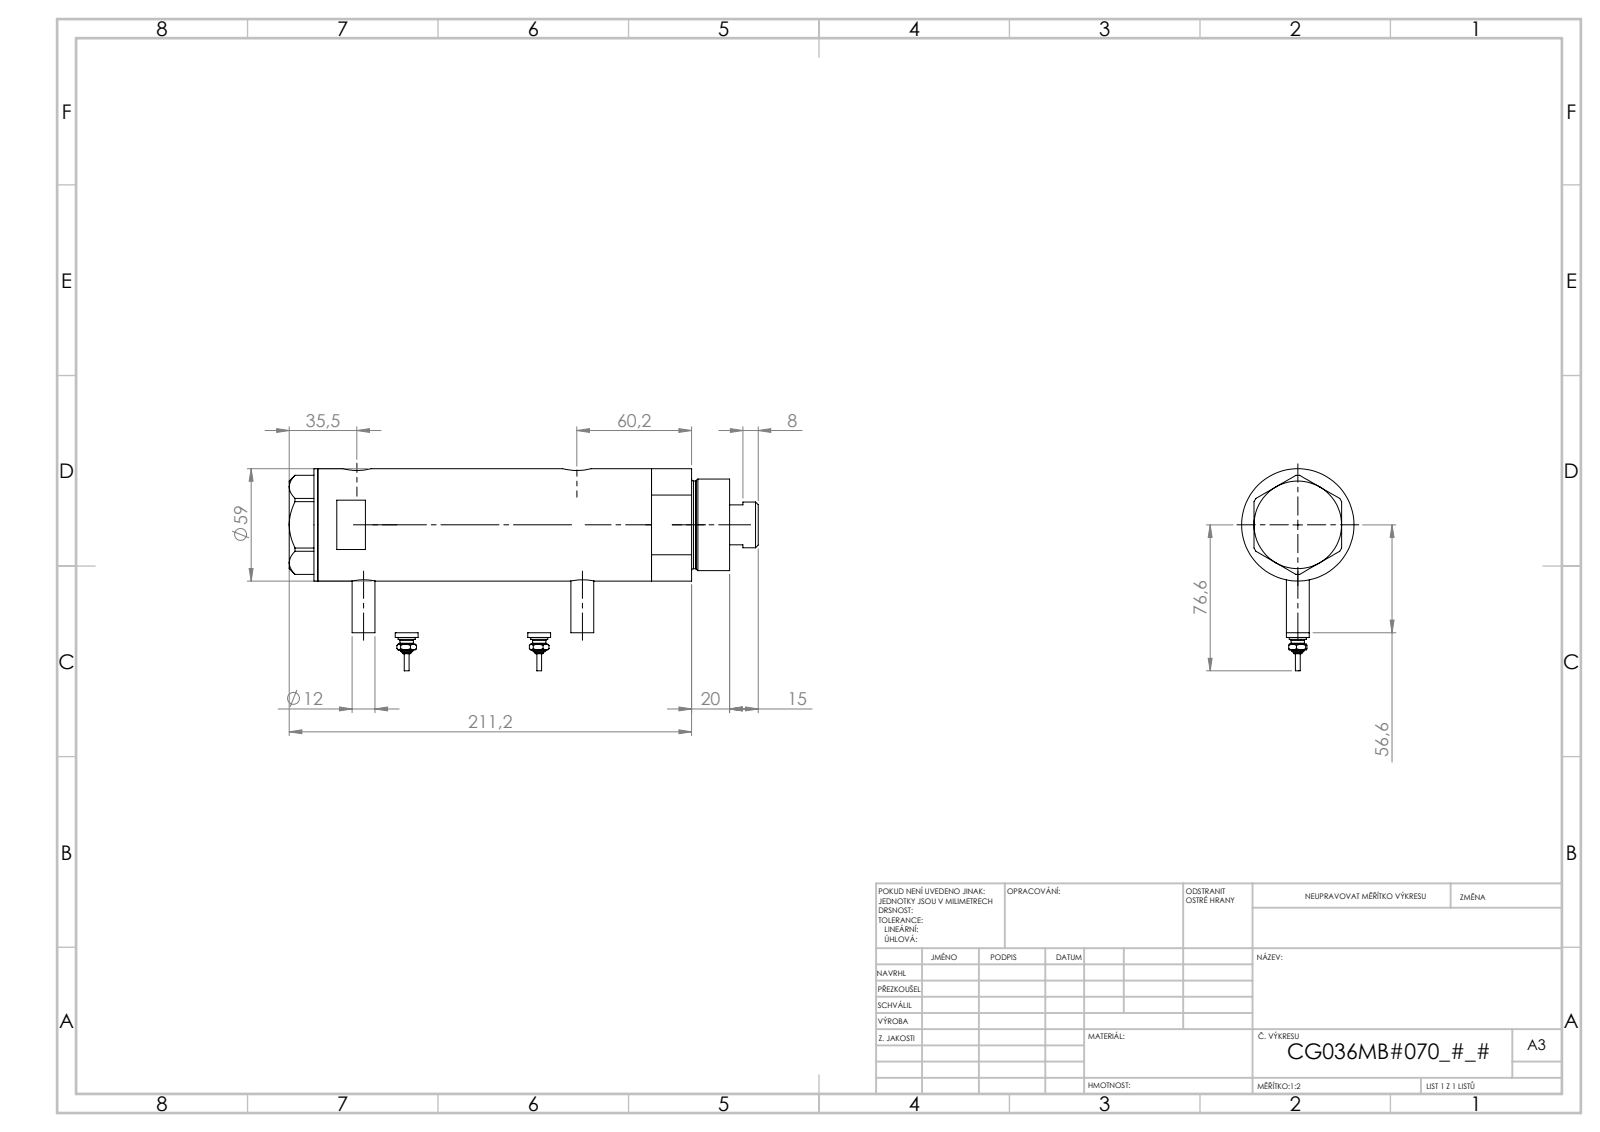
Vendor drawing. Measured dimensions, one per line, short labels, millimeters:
name: V270CG_SWITCH; V270CG_MIDDLE; V270CG_FRONT; V270CG_BACK (+1 more)
written by: SolidWorks 2019 (CONFIG_CONTROL_DESIGN)
unit: mm
bodies: 6 solids, 232 faces (81 planar, 77 cylindrical, 74 other)
size: 233.42 × 91.3 × 59
volume: 528 486 mm³; area: 110 229 mm²
holes: 2× ⌀5, 2× ⌀9.73, 2× ⌀12.5, 2× ⌀15, 1× ⌀8.5, 1× ⌀25, 1× ⌀26.5, 1× ⌀36, 1× ⌀40, 1× ⌀52
bosses: 4× ⌀12, 2× ⌀9, 2× ⌀7, 2× ⌀4.34, 2× ⌀2.4, 1× ⌀59, 1× ⌀48, 1× ⌀46
face distances: 127.34, 23.5, 103.84, 15, 38.5, 142.34, 218.42, 203.42, 179.92, 76.08
hole spacings: 2.9, 3.5, 102.15, 105.05, 105.65, 108.55, 2.89, 2.91
